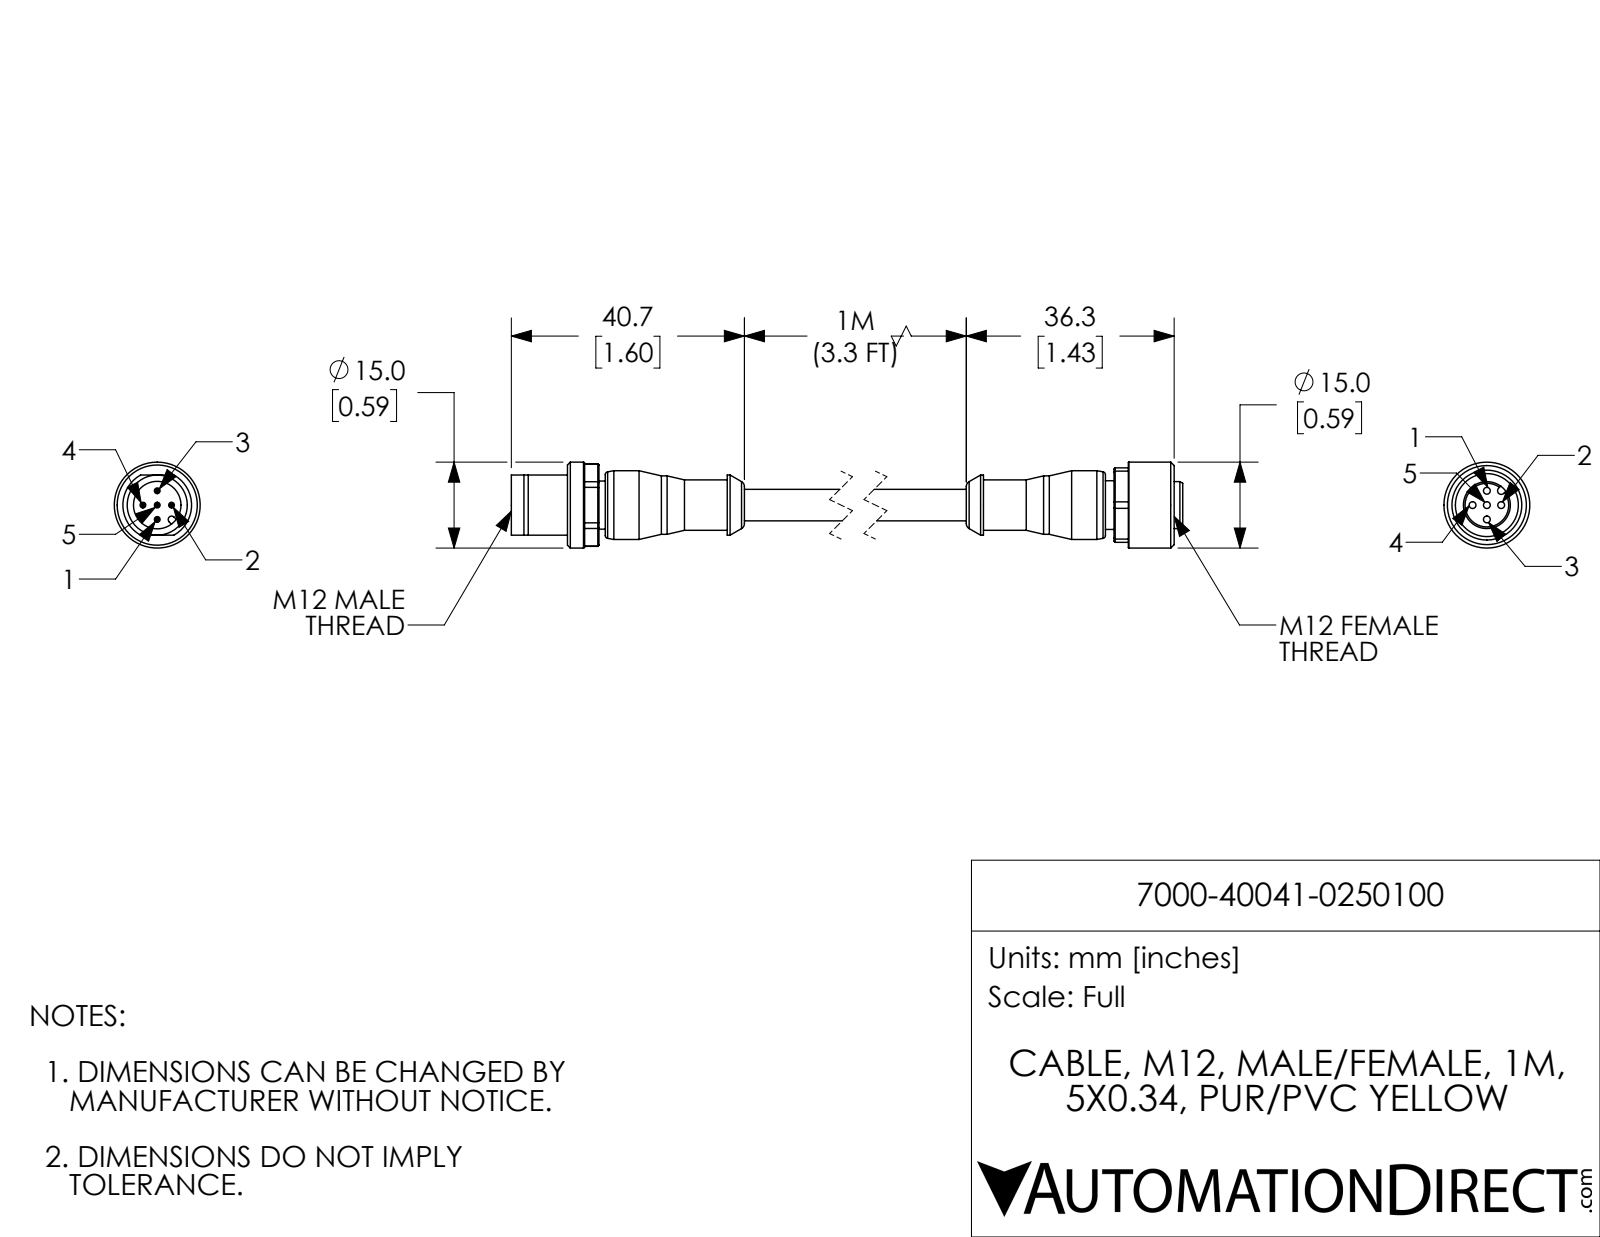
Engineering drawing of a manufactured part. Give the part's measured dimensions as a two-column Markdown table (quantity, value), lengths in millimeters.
| quantity | value |
| --- | --- |
| part name | 7000-40041-0250100; 7000-40041-0250100_FEMALE; 7000-40041-0250100_MALE |
| STEP written by | SolidWorks 2017 (AUTOMOTIVE_DESIGN) |
| units | millimeters |
| bodies | 2 solids, 196 faces (60 planar, 73 cylindrical, 63 other) |
| overall size | 130.5 × 15 × 15 |
| volume | 8 000 mm³ |
| surface area | 5 164 mm² |
| round holes (diameter × count) | 1.2 × 5, 8.3 × 1, 11 × 1 |
| round bosses / shafts (diameter × count) | 1 × 5, 15 × 1, 12 × 1, 10.5 × 1, 10.2 × 1, 8.8 × 1, 8.5 × 1, 8.4 × 1 |
| partial cylindrical surfaces (radius × count) | 0.6 × 1, 0.7 × 1, 7.2 × 1 |
| main face-to-face distances | 12, 13, 3, 103.2, 10.5, 112.6, 56.3, 108.7, 7.5, 1.5 |
| hole center spacings | 2.5, 3.5, 5 |
